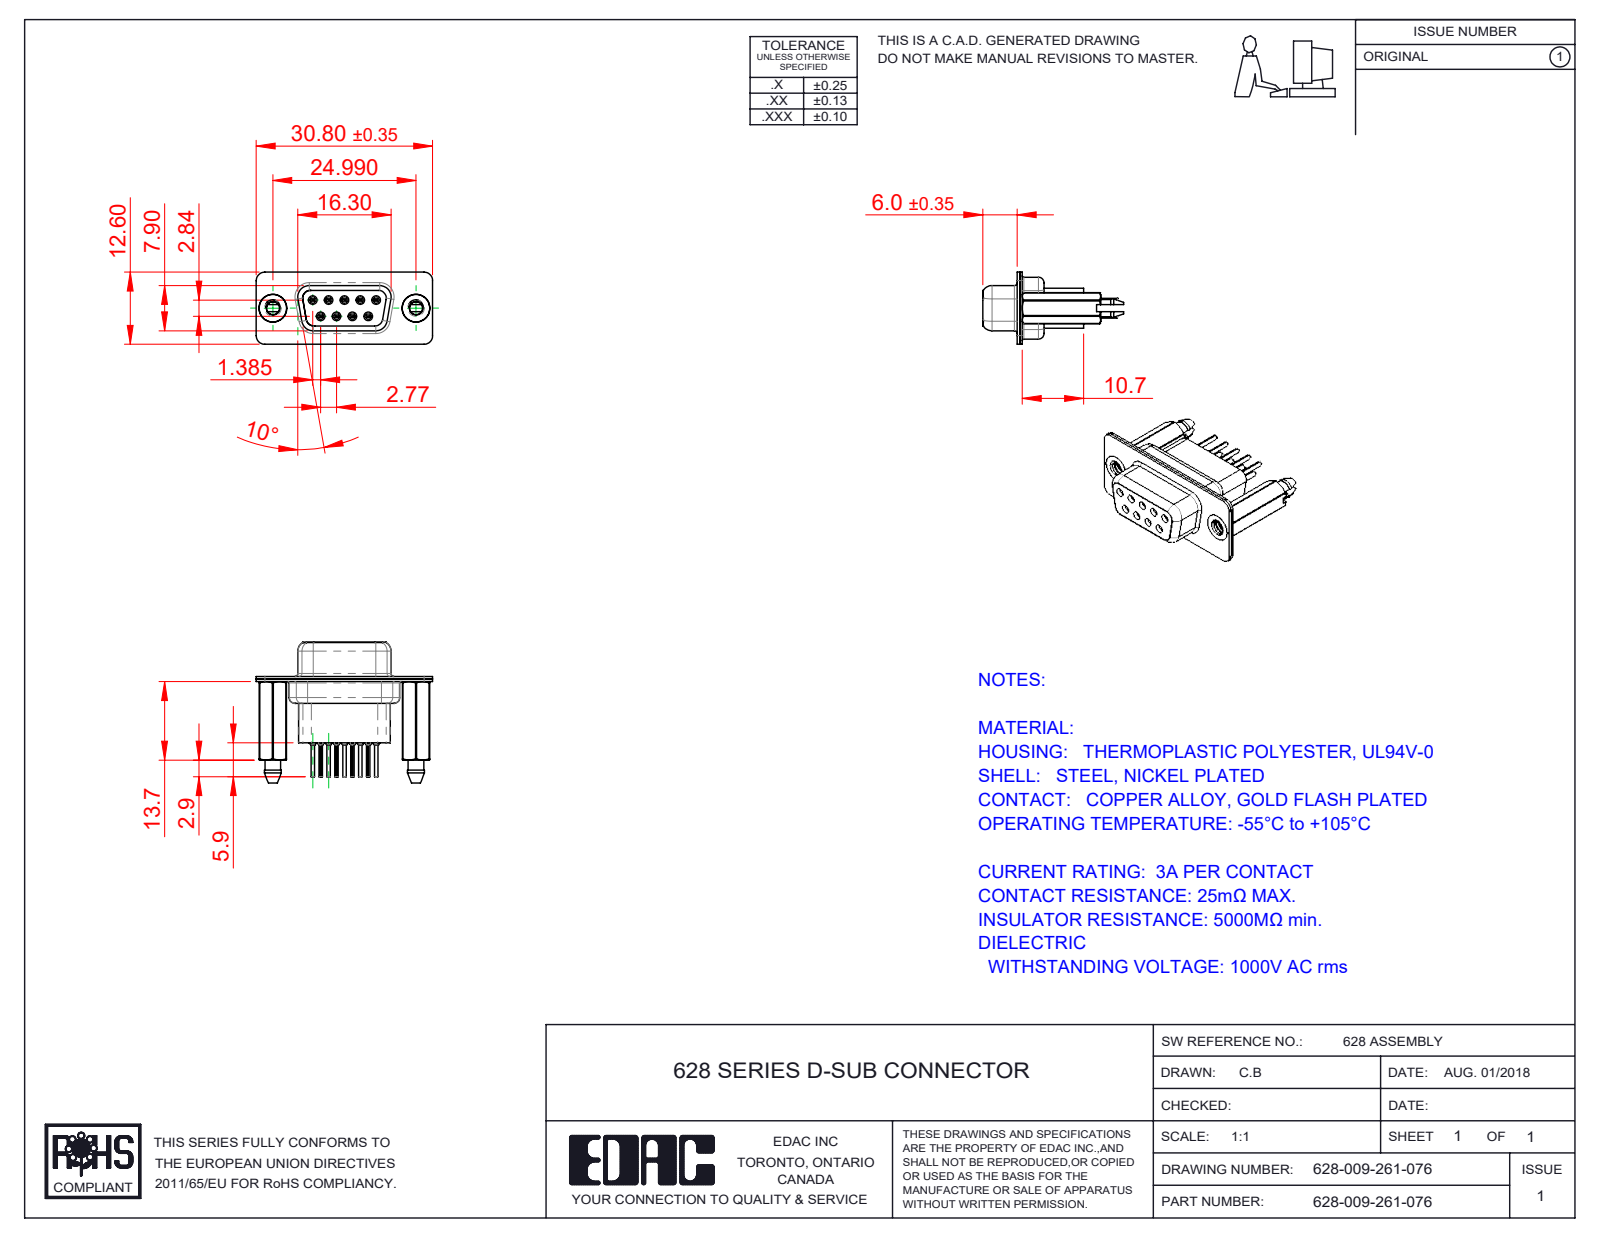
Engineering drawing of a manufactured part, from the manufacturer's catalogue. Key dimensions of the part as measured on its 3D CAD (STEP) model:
Part name (STEP PRODUCT): 628 Shell Rear_09 Contacts; 628 Shell Front_09 Contacts; 628 Housing_09 HP; 628 Contact Row 2_61 (+3 more)
STEP written by: SolidWorks 2020 (CONFIG_CONTROL_DESIGN)
Units: millimetres
Bodies: 14 solids, 1460 faces (378 planar, 466 cylindrical, 616 other)
Overall size (bounding box): 30.8 × 24.6 × 12.6
Volume: 2 591 mm³ · Surface area: 6 029 mm²
Round holes (diameter × count): ⌀0.2 ×9, ⌀0.8 ×9, ⌀0.9 ×9, ⌀1.1 ×9, ⌀1.6 ×9, ⌀1.7 ×5, ⌀2.26 ×2, ⌀4 ×2, ⌀4.05 ×2, ⌀4.85 ×2
Round bosses / shafts (diameter × count): ⌀2 ×9, ⌀1.5 ×9, ⌀1.2 ×9, ⌀0.6 ×9, ⌀4.95 ×2, ⌀4.8 ×2
Partial cylindrical surfaces — rounded edges, fillets, slot ends (radius × count): R1.5 ×19, R0.1 ×18, R2 ×12, R0.28 ×9, R1.35 ×6, R1.6 ×6, R0.25 ×4, R0.5 ×4
Main face-to-face distances: 0.45, 0.4, 0.9, 8.5, 6.6, 1.9, 1.4, 4.76, 7, 10.7
Hole centre spacings: 3.16, 2.77, 5.54, 5.03, 5.04, 8.31, 7.48, 7.49
